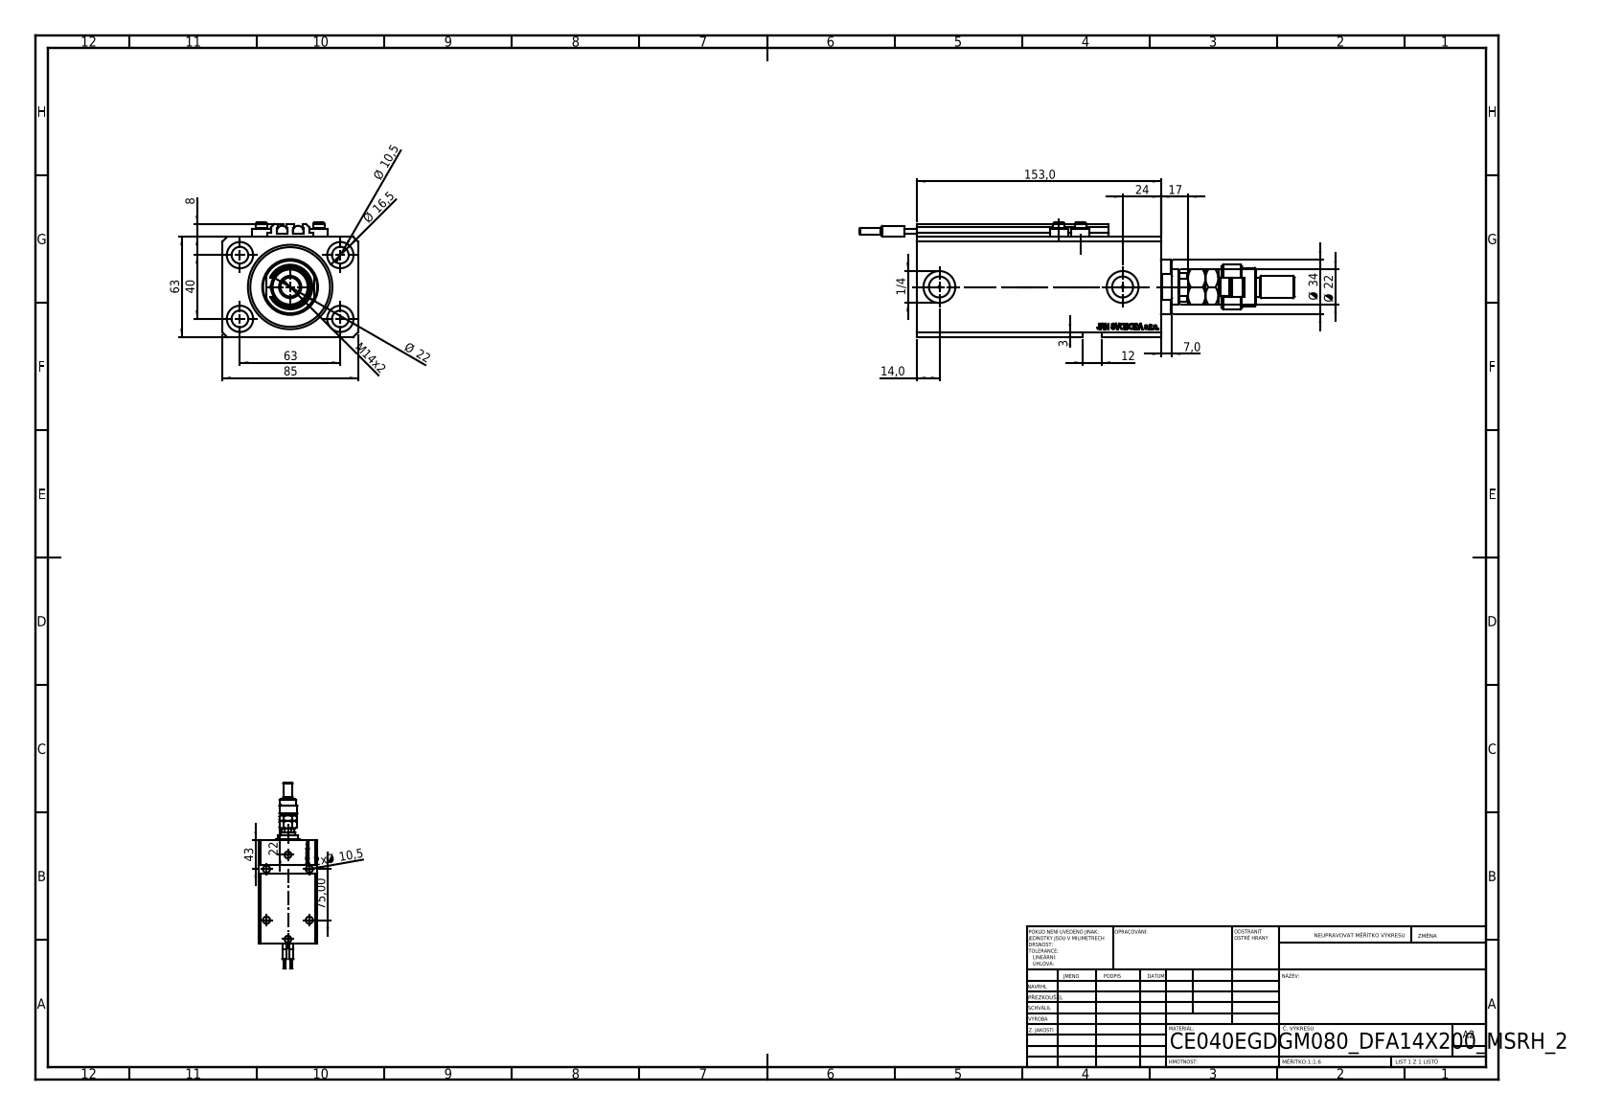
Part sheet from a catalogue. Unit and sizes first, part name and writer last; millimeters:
Units: millimetres
Overall size (bounding box): 273 × 85 × 72
Round holes (diameter × count): ⌀10.5 ×8, ⌀1.25 ×4, ⌀4 ×4, ⌀16.5 ×4, ⌀10 ×2, ⌀13.16 ×2, ⌀20 ×2, ⌀12.5 ×1, ⌀22 ×1, ⌀40 ×1, ⌀53 ×1
Round bosses / shafts (diameter × count): ⌀11.6 ×4, ⌀7 ×4, ⌀6.8 ×2, ⌀6.5 ×2, ⌀4 ×2, ⌀34 ×1, ⌀28 ×1, ⌀24 ×1
Partial cylindrical surfaces — rounded edges, fillets, slot ends (radius × count): R0.2 ×10, R9.75 ×1, R10.5 ×1
Main face-to-face distances: 63, 85, 17, 153, 136, 3, 65, 11.4, 124.6, 141.6
Hole centre spacings: 37.31, 63, 13.6, 15.4, 24.96, 33.62, 36, 37.86
Volume: 171 530 mm³ · Surface area: 152 690 mm²
Bodies: 11 solids, 1260 faces (599 planar, 183 cylindrical, 478 other)
Part name (STEP PRODUCT): SWITCH_V250CE; V250CE_VC_E; FEMALE_PART_FOR_DFA; V250CE_C_VCP (+3 more)
STEP written by: SolidWorks 2019 (CONFIG_CONTROL_DESIGN)
